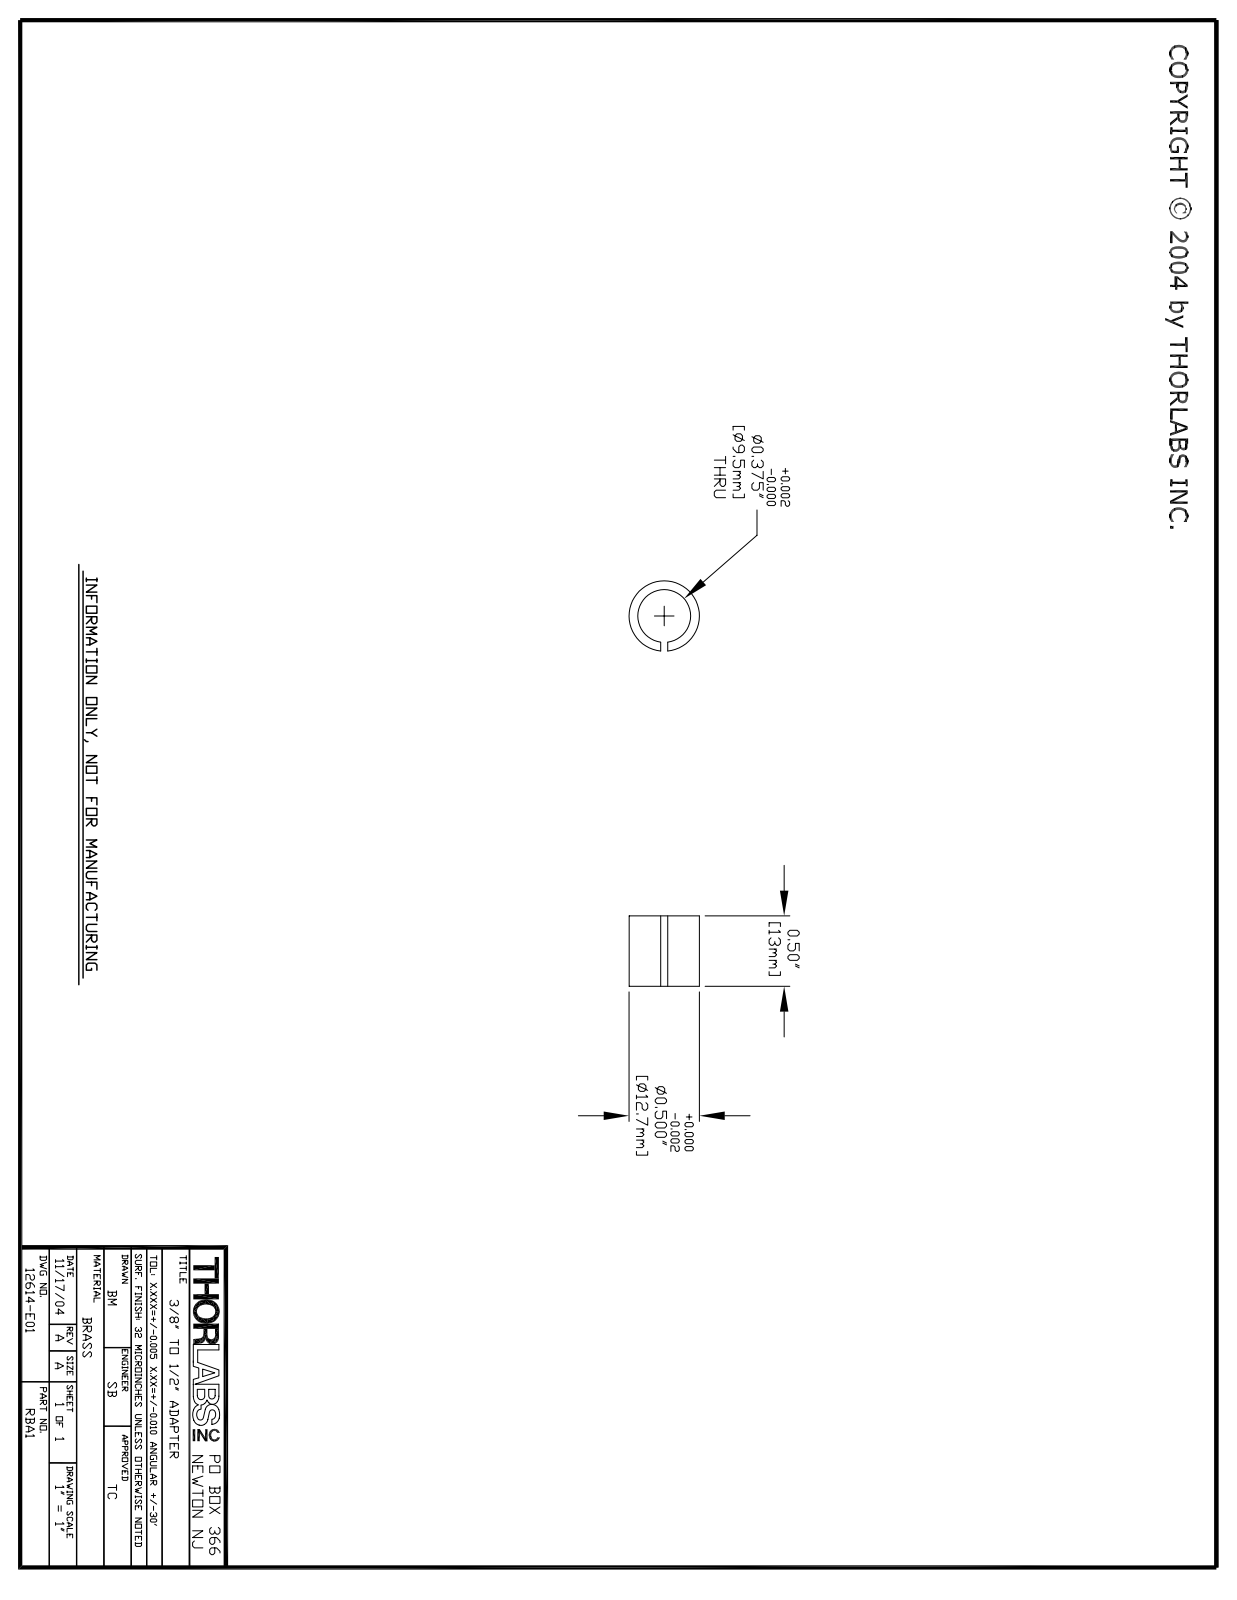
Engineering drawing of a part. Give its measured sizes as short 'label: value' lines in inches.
name: 12614-E0W
written by: SolidWorks 2011 (CONFIG_CONTROL_DESIGN)
unit: in
bodies: 1 solid, 10 faces (4 planar, 6 cylindrical, 0 other)
size: 0.5 × 0.499 × 0.498
volume: 0.041 in³; area: 1.549 in²
holes: 1× ⌀0.376
bosses: 1× ⌀0.499
face distances: 0.5, 0.05
